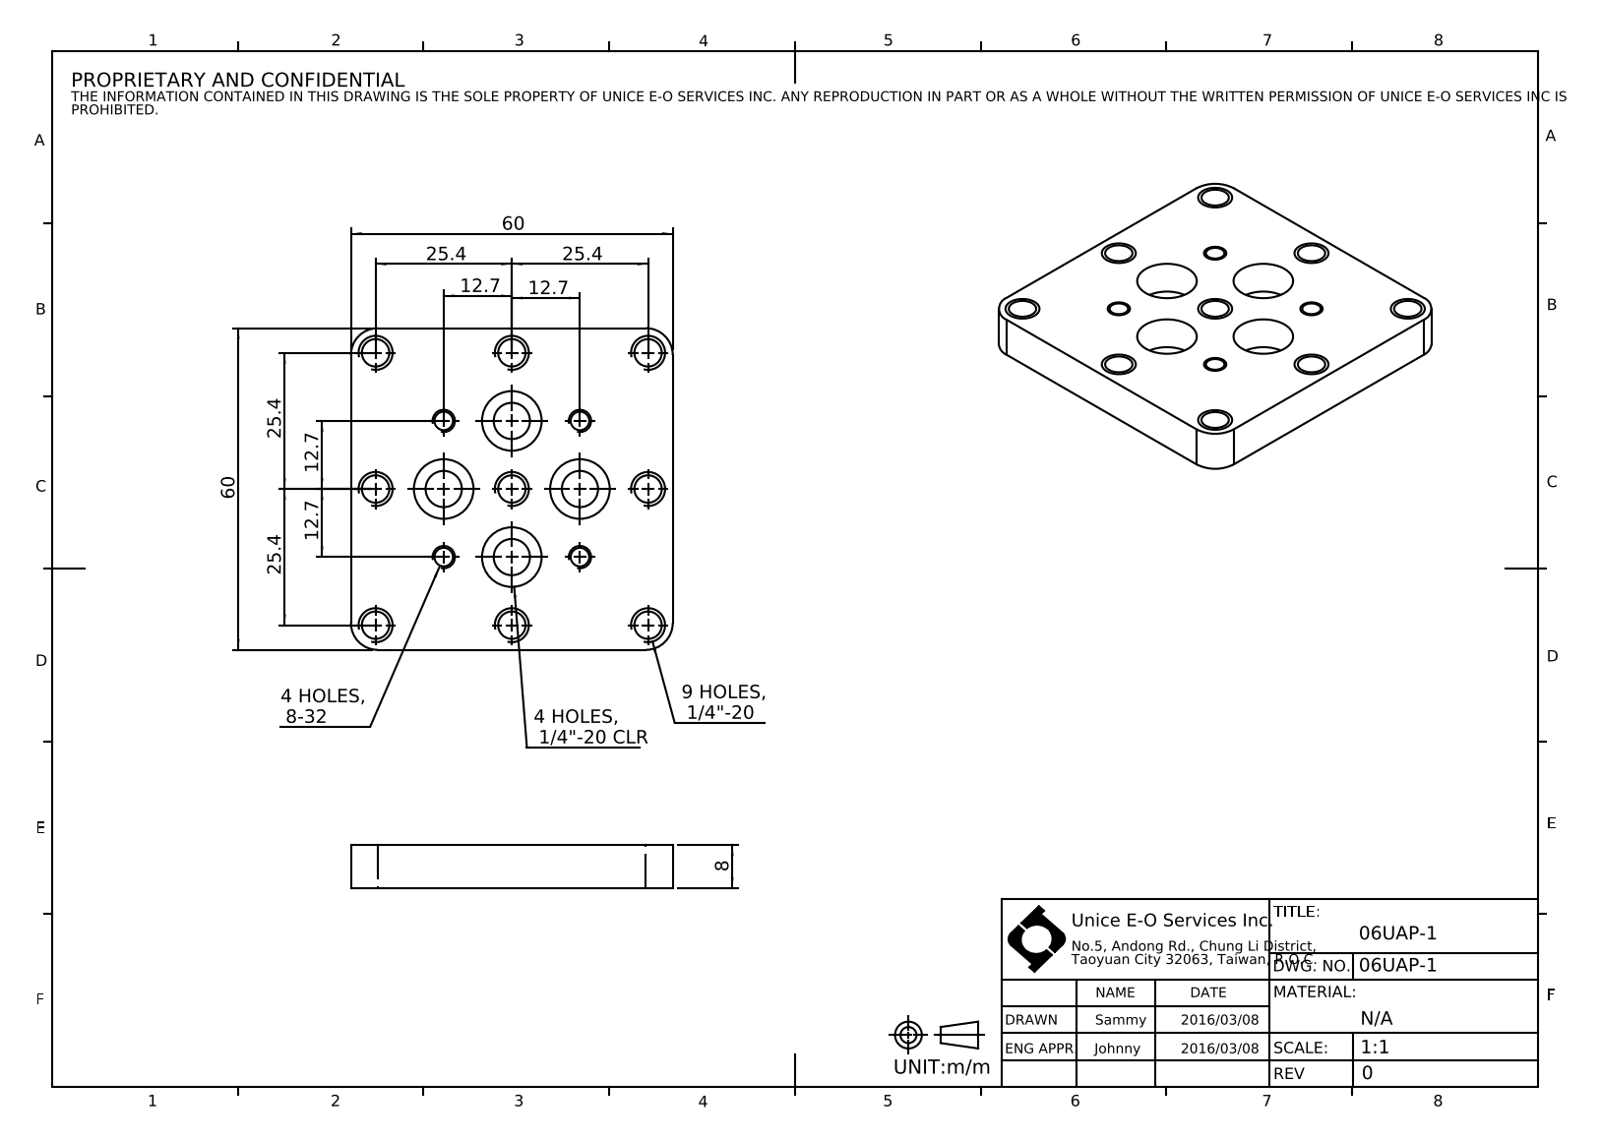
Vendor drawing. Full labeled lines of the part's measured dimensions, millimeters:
Part name (STEP PRODUCT): 06UAP-1
STEP written by: SolidWorks 2016 (CONFIG_CONTROL_DESIGN)
Units: millimetres
Bodies: 1 solid, 56 faces (10 planar, 46 cylindrical, 0 other)
Overall size (bounding box): 60 × 60 × 8
Volume: 24 154 mm³ · Surface area: 10 807 mm²
Round holes (diameter × count): ⌀5.11 ×9, ⌀3.45 ×4, ⌀6.76 ×4, ⌀11.11 ×4
Partial cylindrical surfaces — rounded edges, fillets, slot ends (radius × count): R5 ×4
Main face-to-face distances: 8, 60, 1.65, 6.35
Hole centre spacings: 28.4, 17.96, 25.4, 12.7, 40.16, 35.92, 45.79, 56.8
